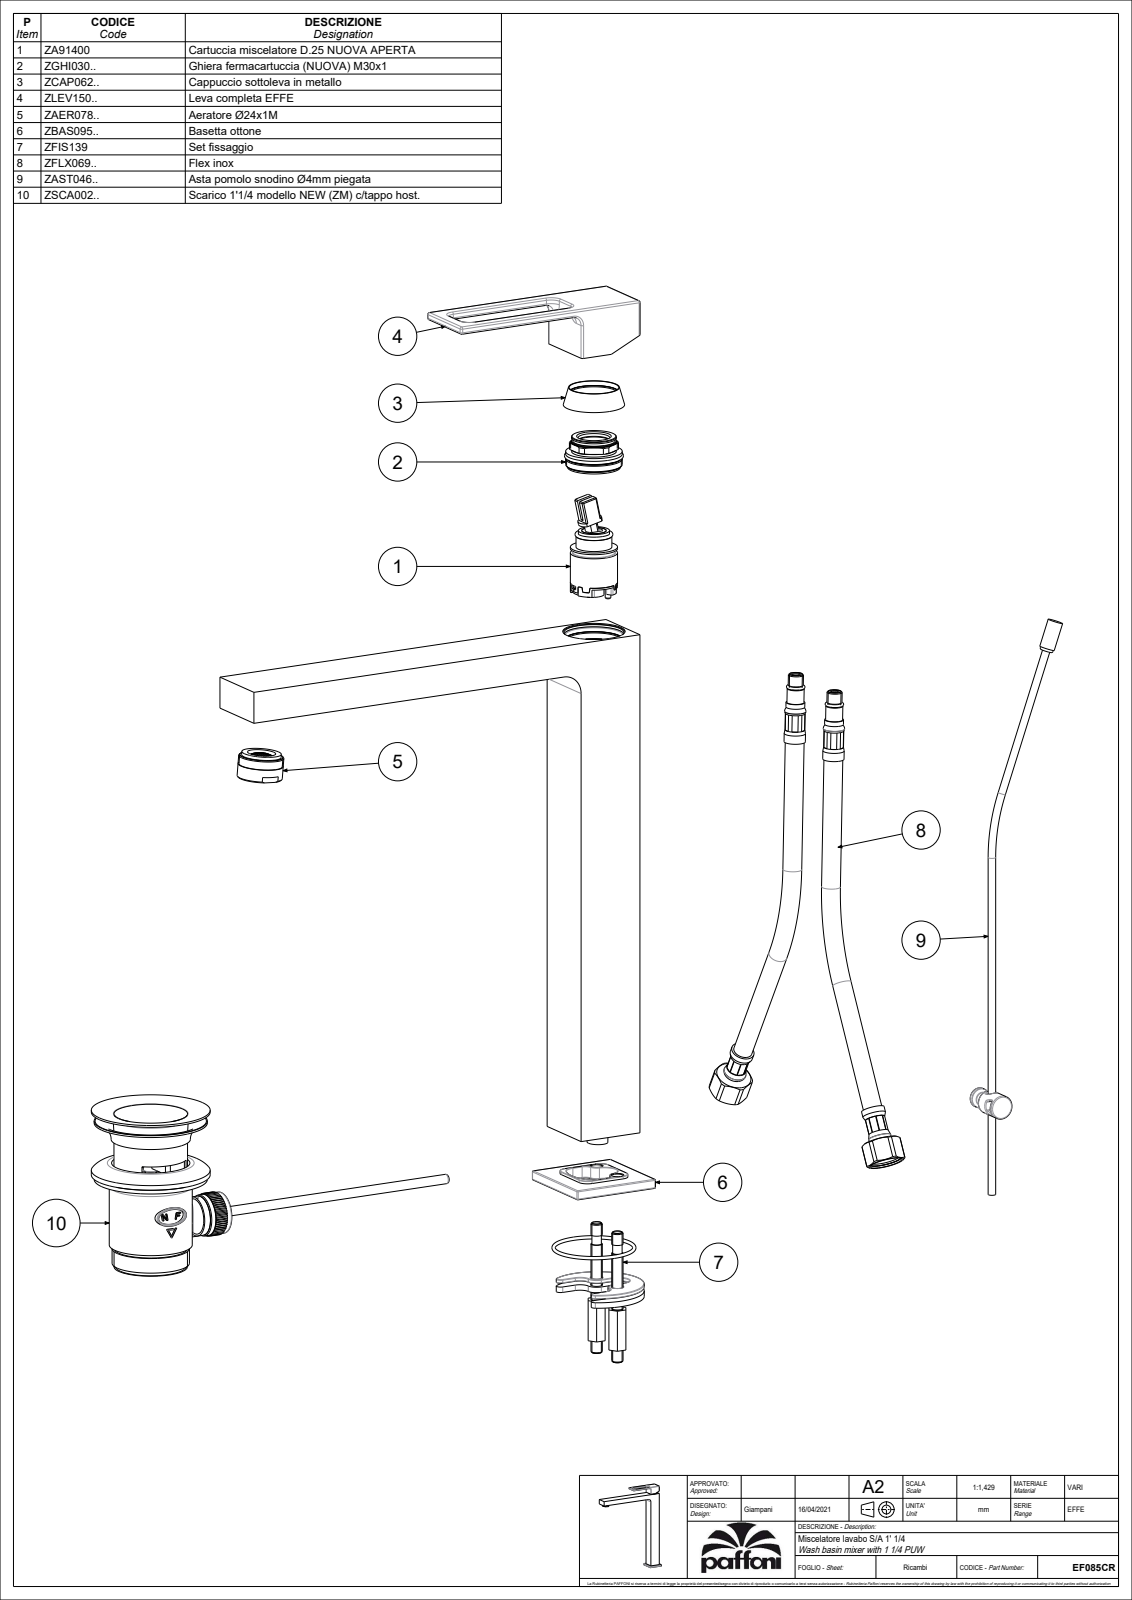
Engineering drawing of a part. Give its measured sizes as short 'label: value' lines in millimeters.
name: EF085CR
written by: CREO PARAMETRIC BY PTC INC, 2020044 (CONFIG_CONTROL_DESIGN)
unit: mm
bodies: 5 solids, 1900 faces (1544 planar, 205 cylindrical, 151 other)
size: 306.78 × 252.56 × 48
volume: 207 030 mm³; area: 135 805 mm²
holes: 4× ⌀5.5, 2× ⌀6.2, 1× ⌀3, 1× ⌀4.2, 1× ⌀4.5, 1× ⌀7.8, 1× ⌀16, 1× ⌀17, 1× ⌀20, 1× ⌀21, 1× ⌀23, 1× ⌀24.5
bosses: 1× ⌀41.8, 1× ⌀24, 1× ⌀19.5, 1× ⌀18.8, 1× ⌀16.8, 1× ⌀8, 1× ⌀7.6, 1× ⌀4
rounds: 66× R1, 14× R0.5, 9× R5, 8× R1.5, 6× R0.25, 4× R7, 2× R3.5, 2× R4
face distances: 3, 36, 33, 14, 30, 2.5, 17, 30.5, 33.5, 11
hole spacings: 11.4, 13.6, 11, 22
